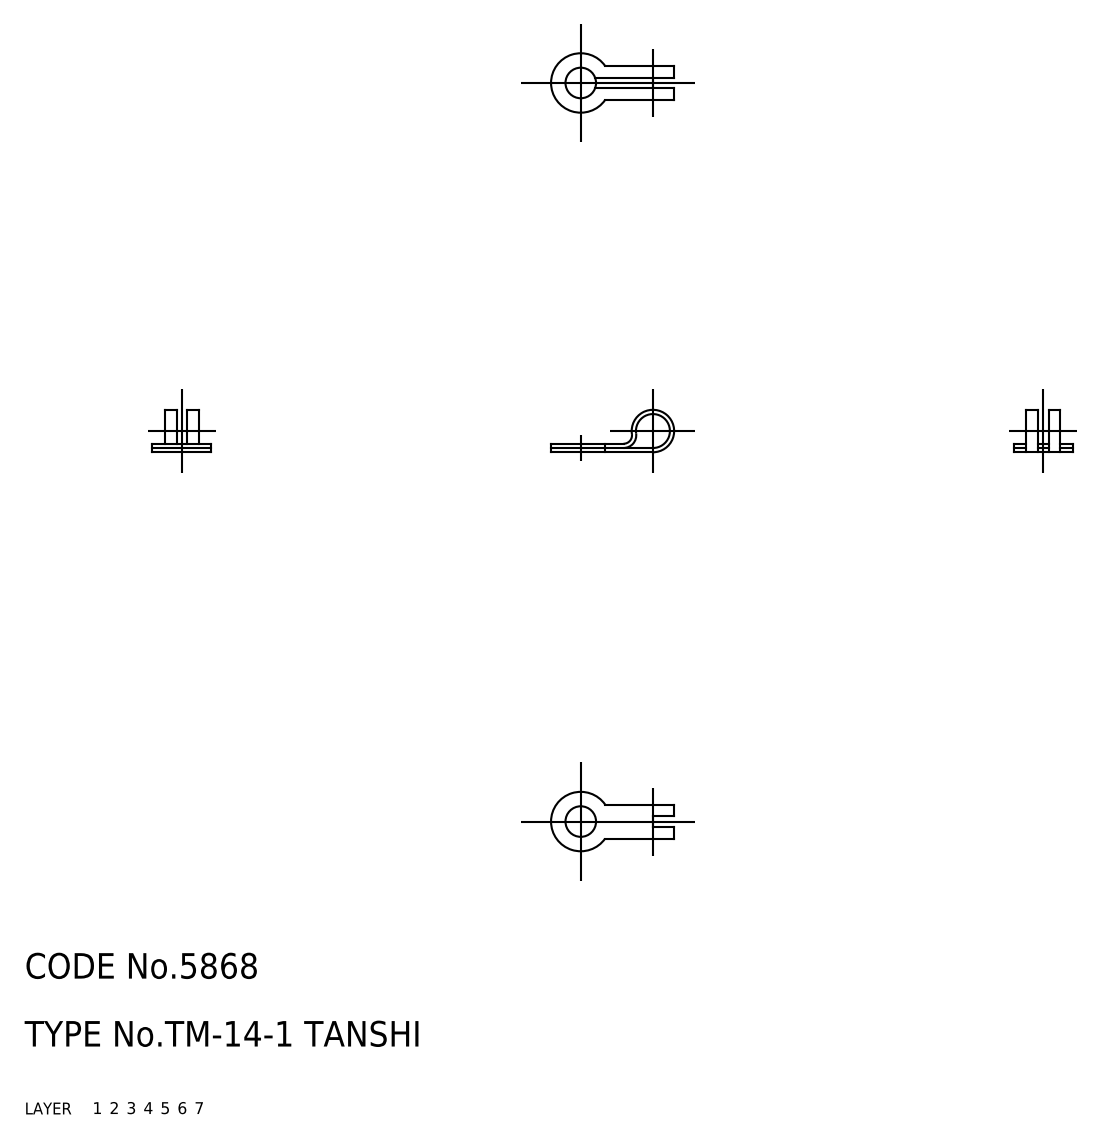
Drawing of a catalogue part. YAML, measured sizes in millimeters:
part_name: "terminal"
step_written_by: "CADfix (AUTOMOTIVE_DESIGN)"
units: millimeters
bodies: {solids: 1, faces: 22, planar: 0, cylindrical: 0, other: 22}
overall_size: [14.5, 7, 5]
volume: 58
surface_area: 300
